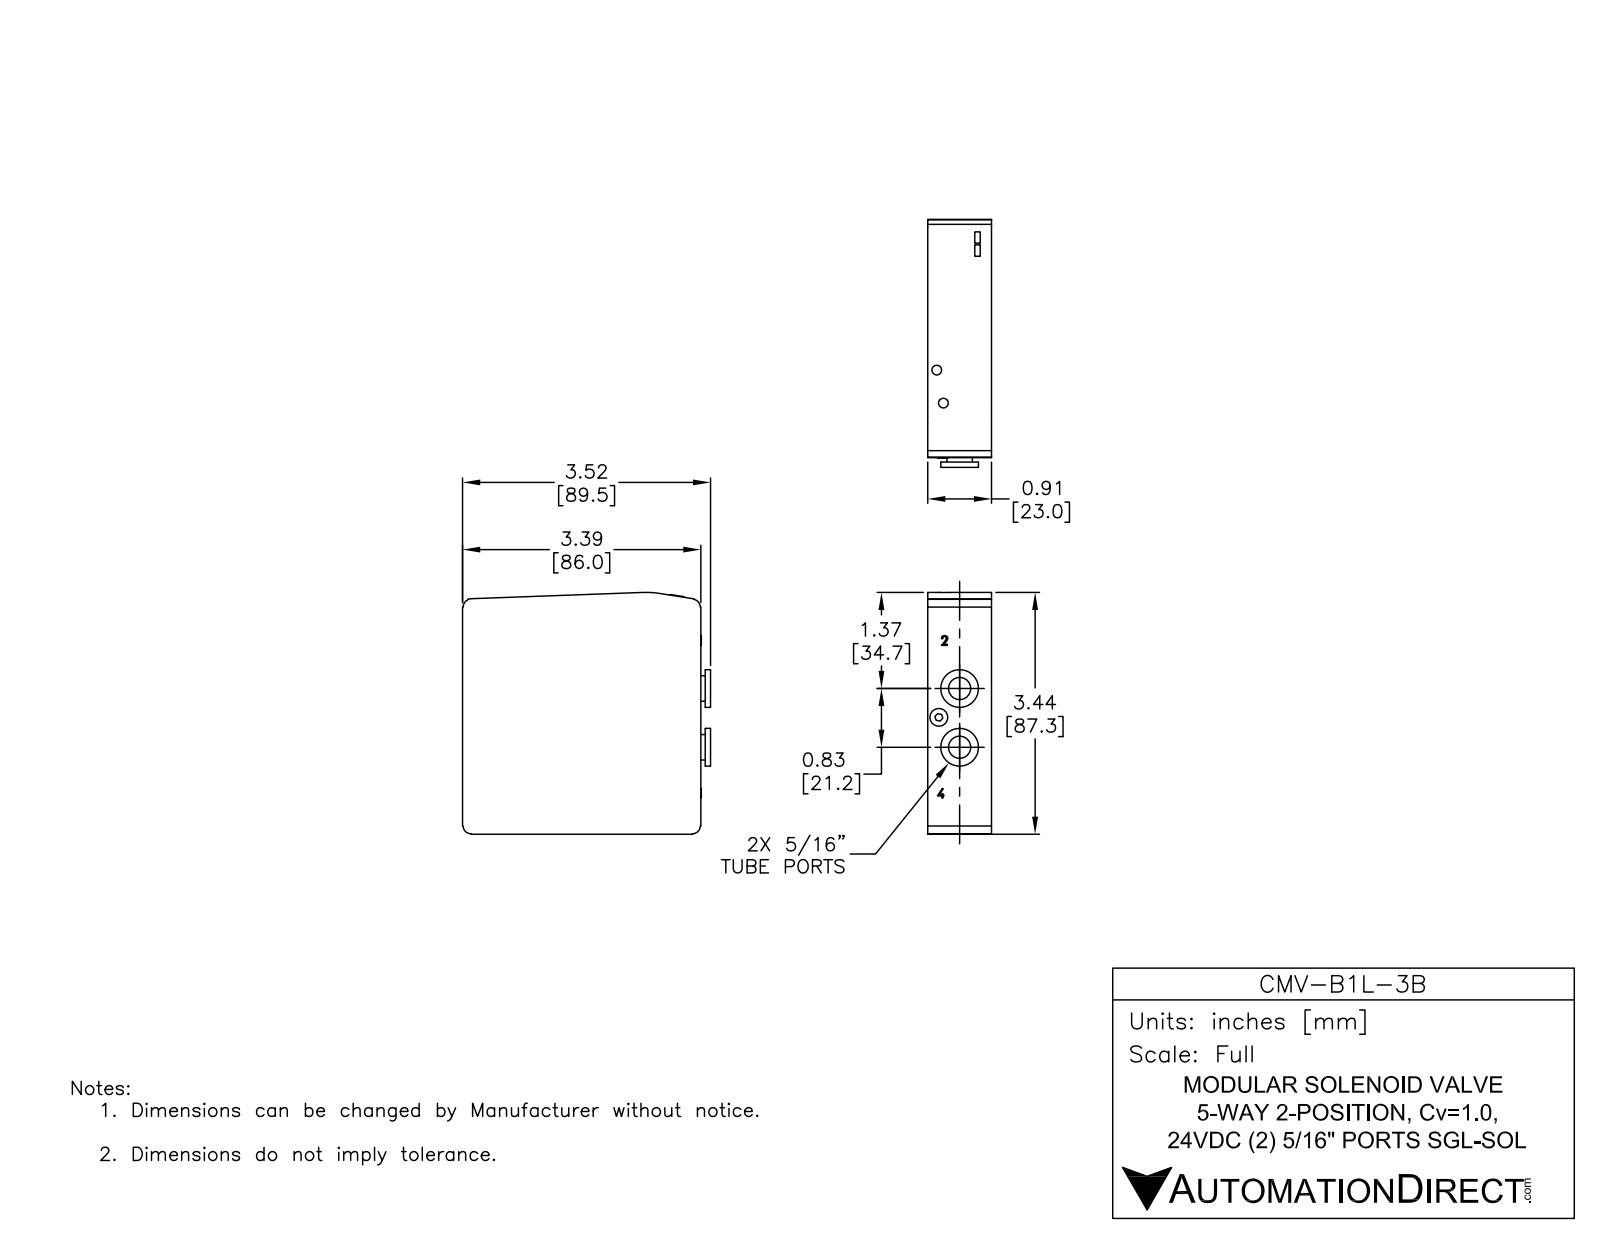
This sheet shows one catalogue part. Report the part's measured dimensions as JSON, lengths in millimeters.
{"part_name": "CMV-B1L-3B", "step_written_by": "SolidWorks 2013 (AUTOMOTIVE_DESIGN)", "units": "millimeters", "bodies": {"solids": 74, "faces": 1156, "planar": 876, "cylindrical": 159, "other": 121}, "overall_size": [89.5, 87.3, 31.43], "volume_mm3": 154043, "surface_area_mm2": 54268, "round_holes": [[4.4, 4], [5.25, 4], [6.5, 2], [9.75, 2], [14, 2], [18, 2], [3.35, 1], [3.6, 1], [6.25, 1], [6.4, 1]], "round_bosses_or_shafts": [[4, 4], [1.5, 4], [15.25, 2], [11, 2], [6.25, 2], [5.75, 2], [4.2, 2], [3.5, 1]], "partial_cylinders_radius": [[2.35, 12], [0.78, 4], [1.5, 4], [2.8, 4], [0.15, 2], [0.25, 2], [1, 2], [0.17, 1]], "face_to_face_distances": [22.5, 12.5, 10, 83, 3, 1, 65.12, 50.25, 32.75, 53.25], "hole_center_spacings": [9.7, 11.99, 12.17, 16, 22.17, 31.45, 31.52, 39.5]}
